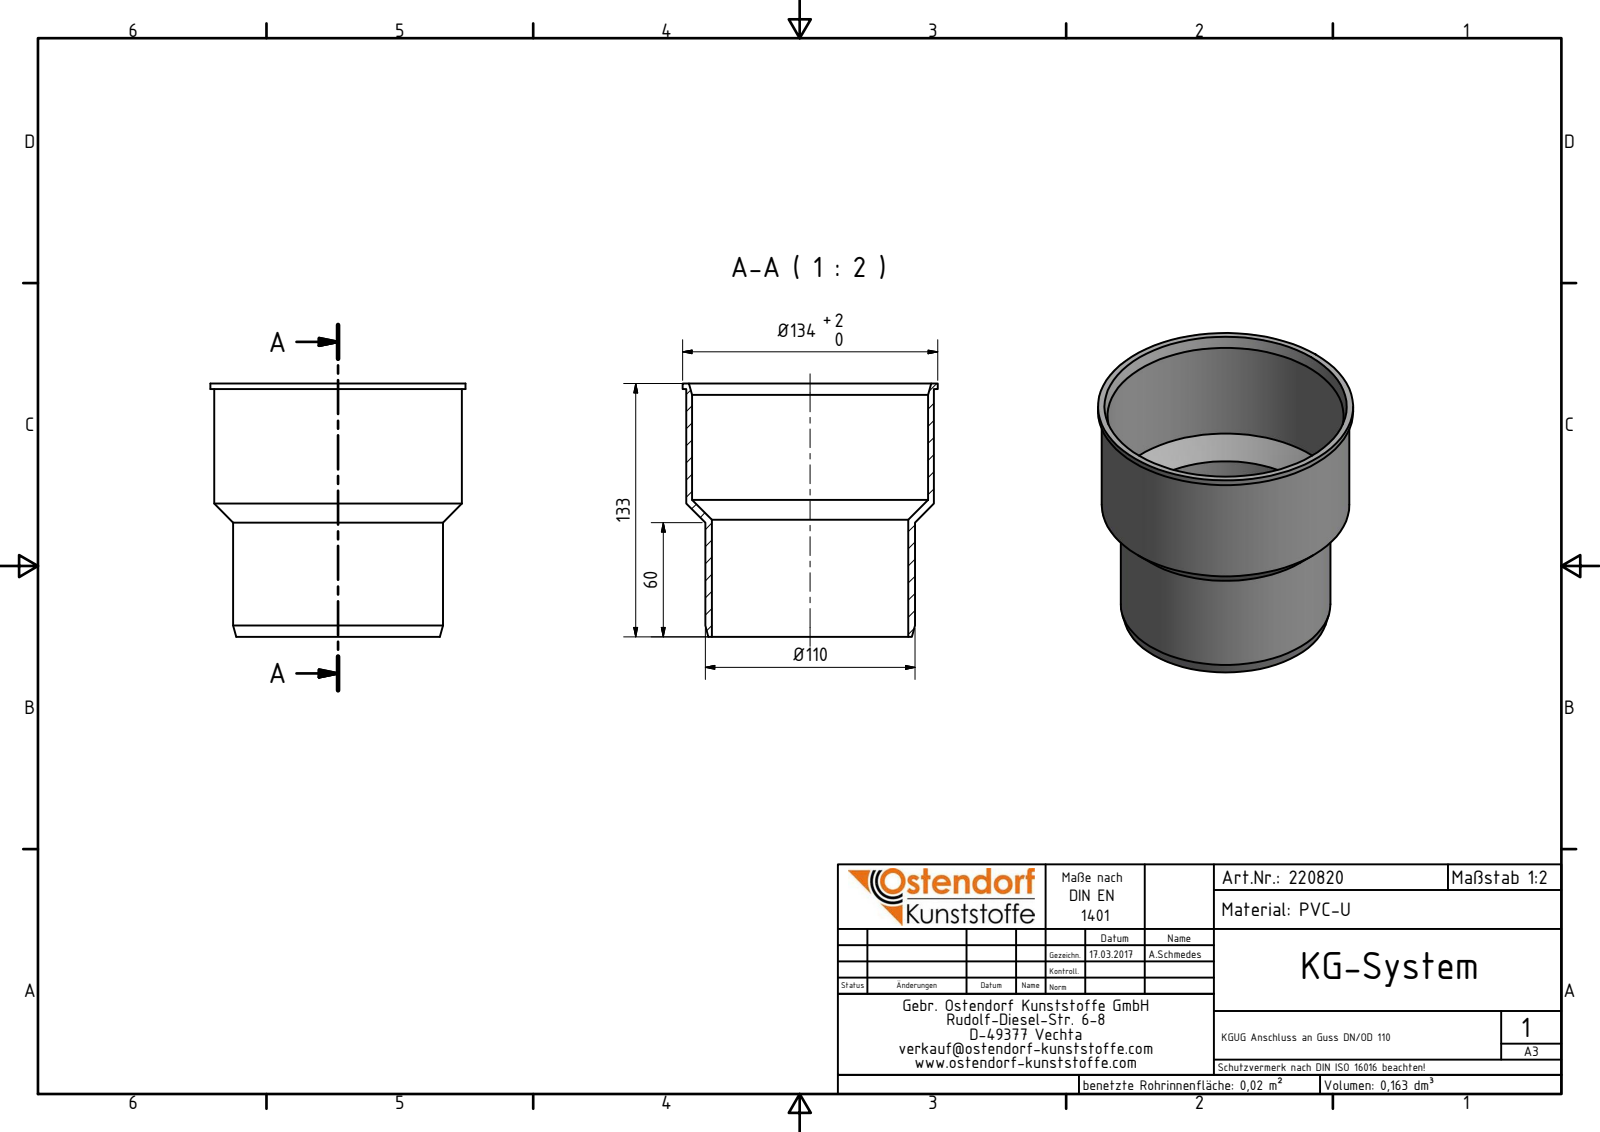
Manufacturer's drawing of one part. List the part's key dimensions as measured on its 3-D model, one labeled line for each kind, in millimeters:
Part name (STEP PRODUCT): 220820 KGUG Anschluss an Guss DN_OD 110
STEP written by: Autodesk Inventor 2016 (AUTOMOTIVE_DESIGN)
Units: millimetres
Bodies: 1 solid, 12 faces (3 planar, 5 cylindrical, 4 other)
Overall size (bounding box): 134 × 134 × 133
Volume: 162 962 mm³ · Surface area: 103 842 mm²
Round holes (diameter × count): ⌀103.15 ×1, ⌀124 ×1
Round bosses / shafts (diameter × count): ⌀134 ×1, ⌀130 ×1, ⌀110.15 ×1
Main face-to-face distances: 3, 130, 133
